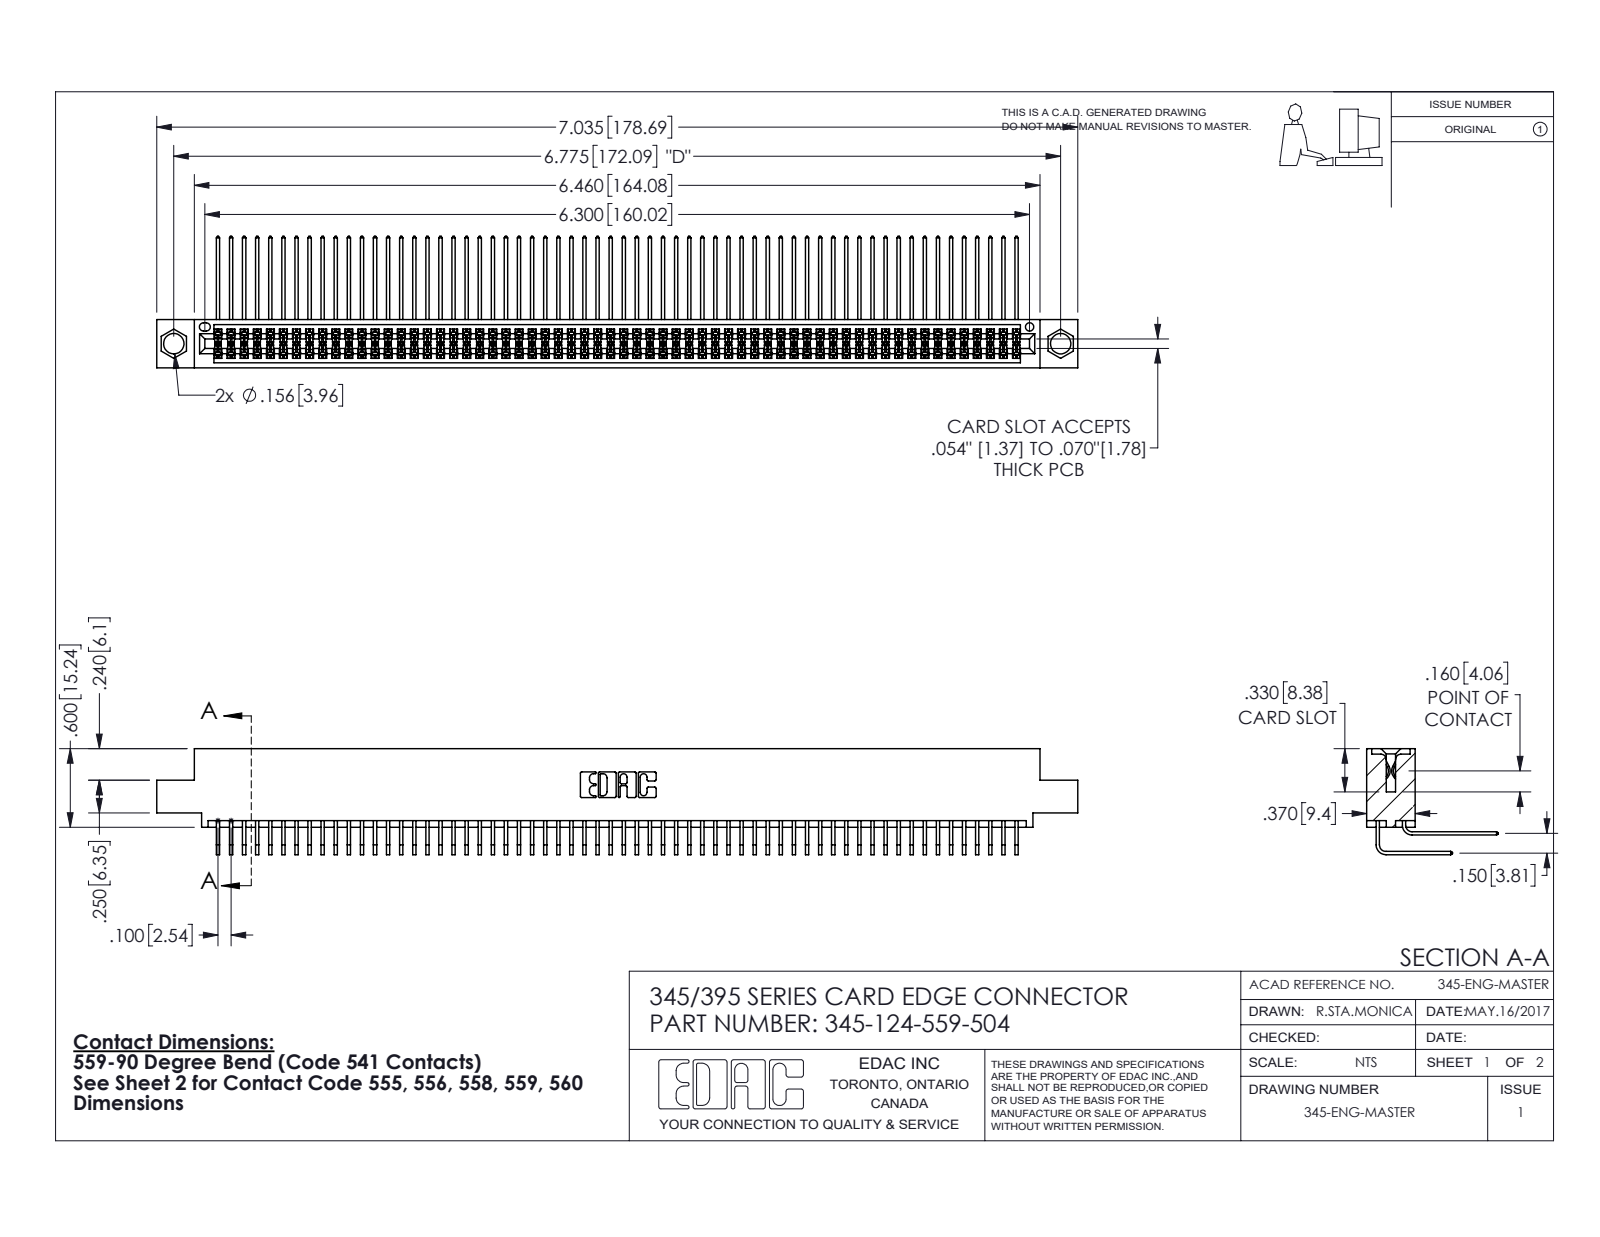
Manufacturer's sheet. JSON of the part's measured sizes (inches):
{"part_name": "345-124-559-504; 345-292-001_558 559 Tail - 1; 345 Part_0.110 Offset - 0.156 Dia-TI; 345-292-001_559 Tail - 2", "step_written_by": "SolidWorks 2020 (CONFIG_CONTROL_DESIGN)", "units": "inches", "bodies": {"solids": 125, "faces": 6592, "planar": 4438, "cylindrical": 2154, "other": 0}, "overall_size": [7.035, 1.005, 0.809], "volume_in3": 1.103, "surface_area_in2": 47.15, "round_holes": [[0.156, 2], [0.064, 1]], "partial_cylinders_radius": [[0.006, 186], [0.01, 22], [0.007, 6], [0.031, 6], [0.026, 3], [0.014, 2], [0.019, 2], [0.022, 2]], "face_to_face_distances": [0.072, 0.298, 0.2, 0.37, 0.098, 0.272, 0.025, 0.225, 0.175, 0.15], "hole_center_spacings": [0.27, 6.539, 6.775]}
